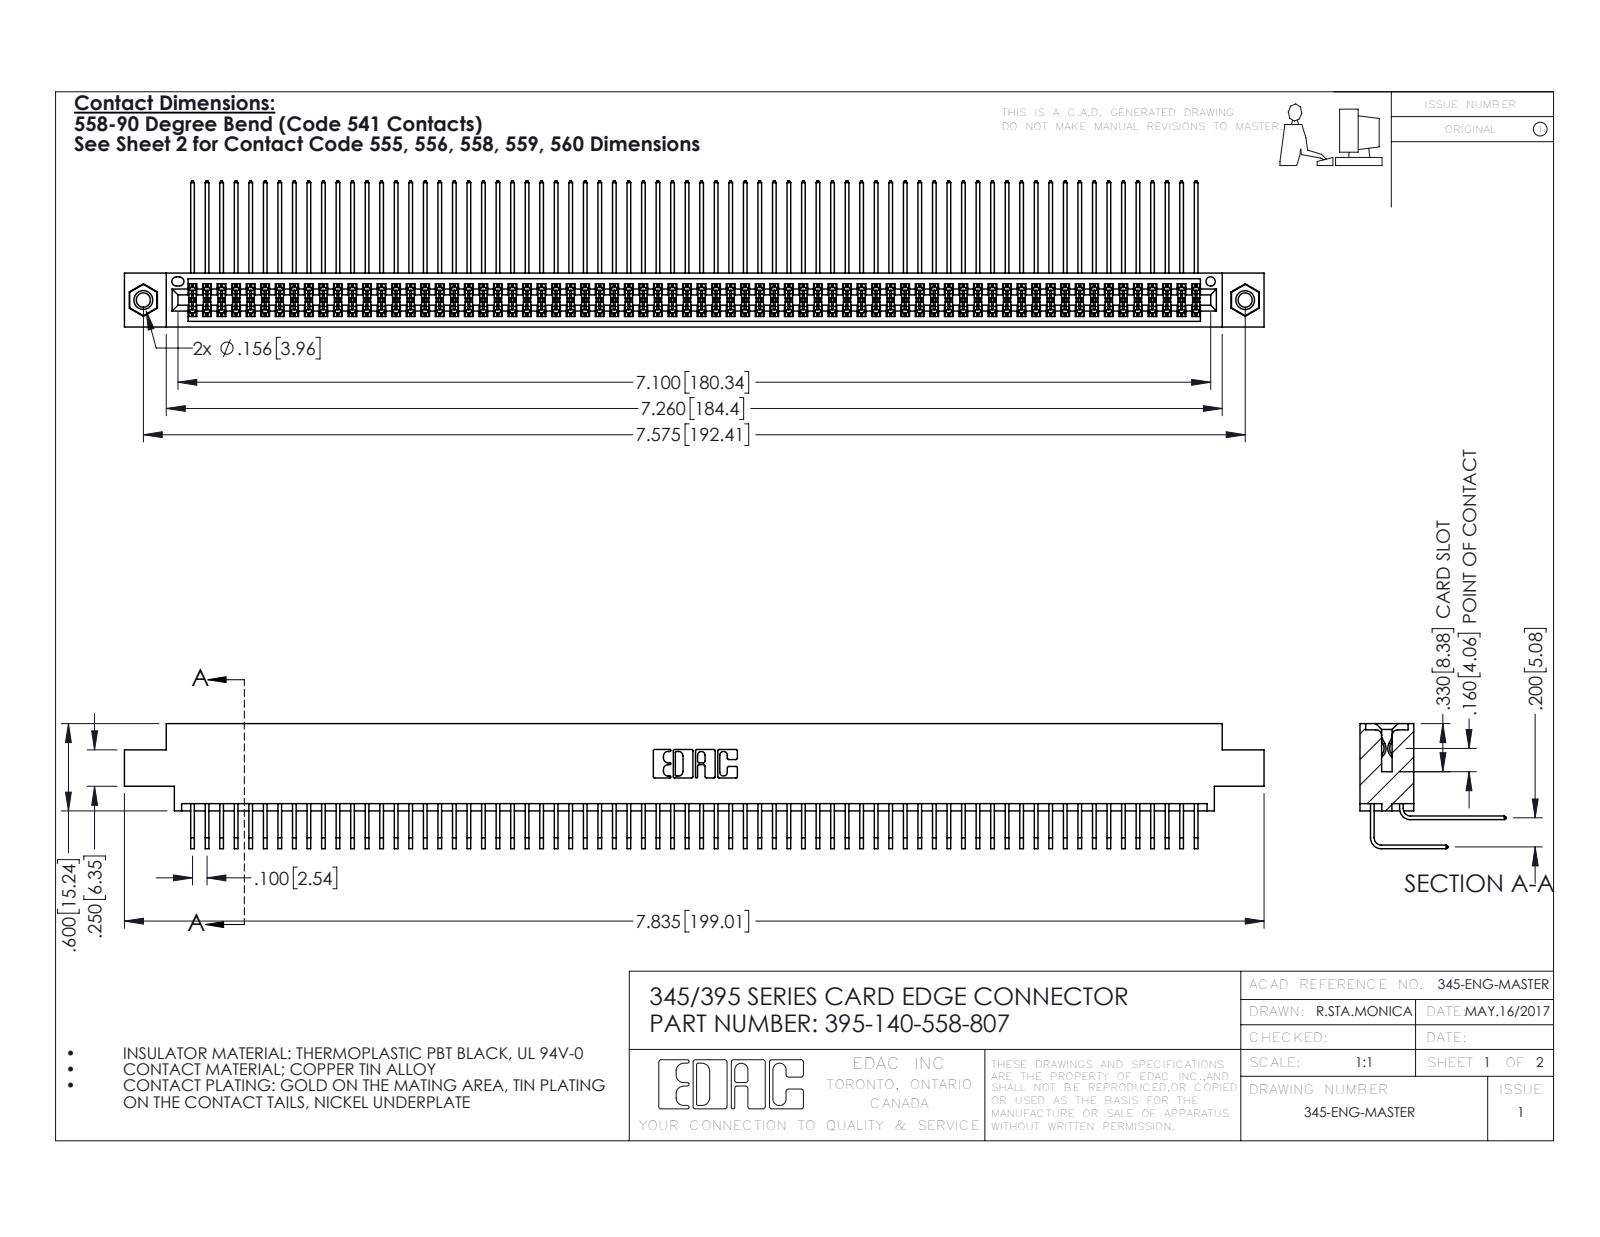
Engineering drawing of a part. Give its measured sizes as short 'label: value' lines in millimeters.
name: 395-140-558-807; 345-250-001_345-250-005-103; 345-292-001_558 Tail - 2; 345-292-001_558 559 Tail - 1 (+1 more)
written by: SolidWorks 2016 (CONFIG_CONTROL_DESIGN)
unit: mm
bodies: 143 solids, 7470 faces (5016 planar, 2438 cylindrical, 16 other)
size: 199 × 25.5 × 21.8
volume: 20 270 mm³; area: 34 480 mm²
holes: 2× ⌀2.5, 2× ⌀3.2, 2× ⌀4, 1× ⌀1.6
bosses: 2× ⌀3.9
rounds: 279× R0.2, 22× R0.3, 6× R0.2, 6× R0.8, 3× R0.7, 2× R0.4, 2× R0.5, 2× R0.6
face distances: 1.8, 7.6, 5.1, 9.4, 2.5, 6.9, 0.6, 5.7, 4.4, 0.6
hole spacings: 6.9, 186.4, 192.4
